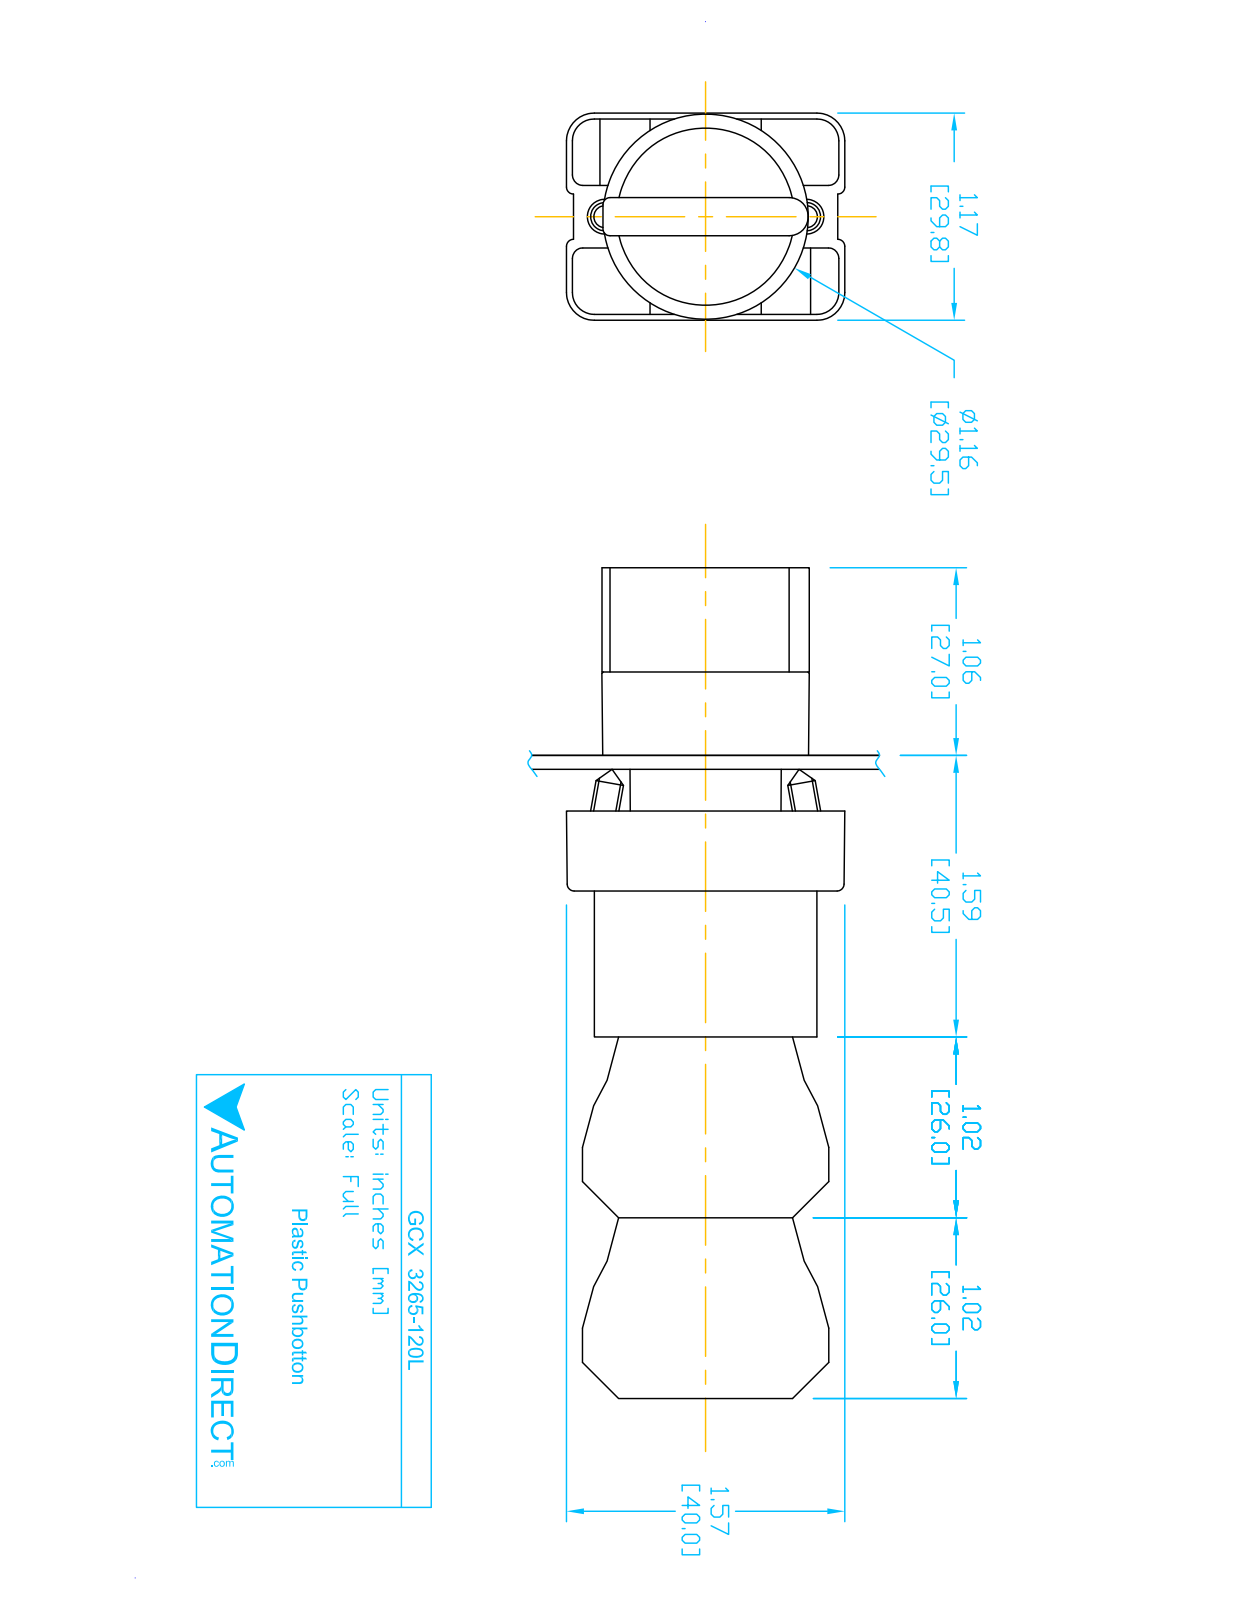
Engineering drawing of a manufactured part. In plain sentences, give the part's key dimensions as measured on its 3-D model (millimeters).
The part is named "ecx1030; ECX3029-2; GCX3265-120L; GCX3265L OPERATOR (+2 more)". Its 3-D file was written by "SolidWorks 2016 (AUTOMOTIVE_DESIGN)". It is 11 solids with 724 faces: 488 planar, 193 cylindrical and 43 other. Overall it measures 118.8 by 40.2 by 29.9 millimeters. Its volume is 77 850 cubic millimeters and its surface area 38 210 square millimeters. Round holes: 4 of diameter 2, 2 of diameter 2.2, 2 of diameter 3.1, 2 of diameter 3.3, 1 of diameter 5, 1 of diameter 11.9, 1 of diameter 22.3, 1 of diameter 22.6, 1 of diameter 26. Round bosses or shafts: 4 of diameter 4, 1 of diameter 29.8, 1 of diameter 25.5, 1 of diameter 24, 1 of diameter 21.7, 1 of diameter 19.8, 1 of diameter 12.8. Partial cylindrical surfaces (rounded edges, fillets, slot ends): 24 of radius 1.5, 12 of radius 1, 12 of radius 3.1, 12 of radius 4, 9 of radius 1, 2 of radius 0.5, 2 of radius 1.6, 2 of radius 2. The main face-to-face distances are 14.7, 15.1, 26, 29.7, 0.4, 21, 47, 77.3, 51.3, 30.3. The hole center spacings are 6, 25.5, 24.7, 12, 13.7, 13.8, 27.5, 12.3.
